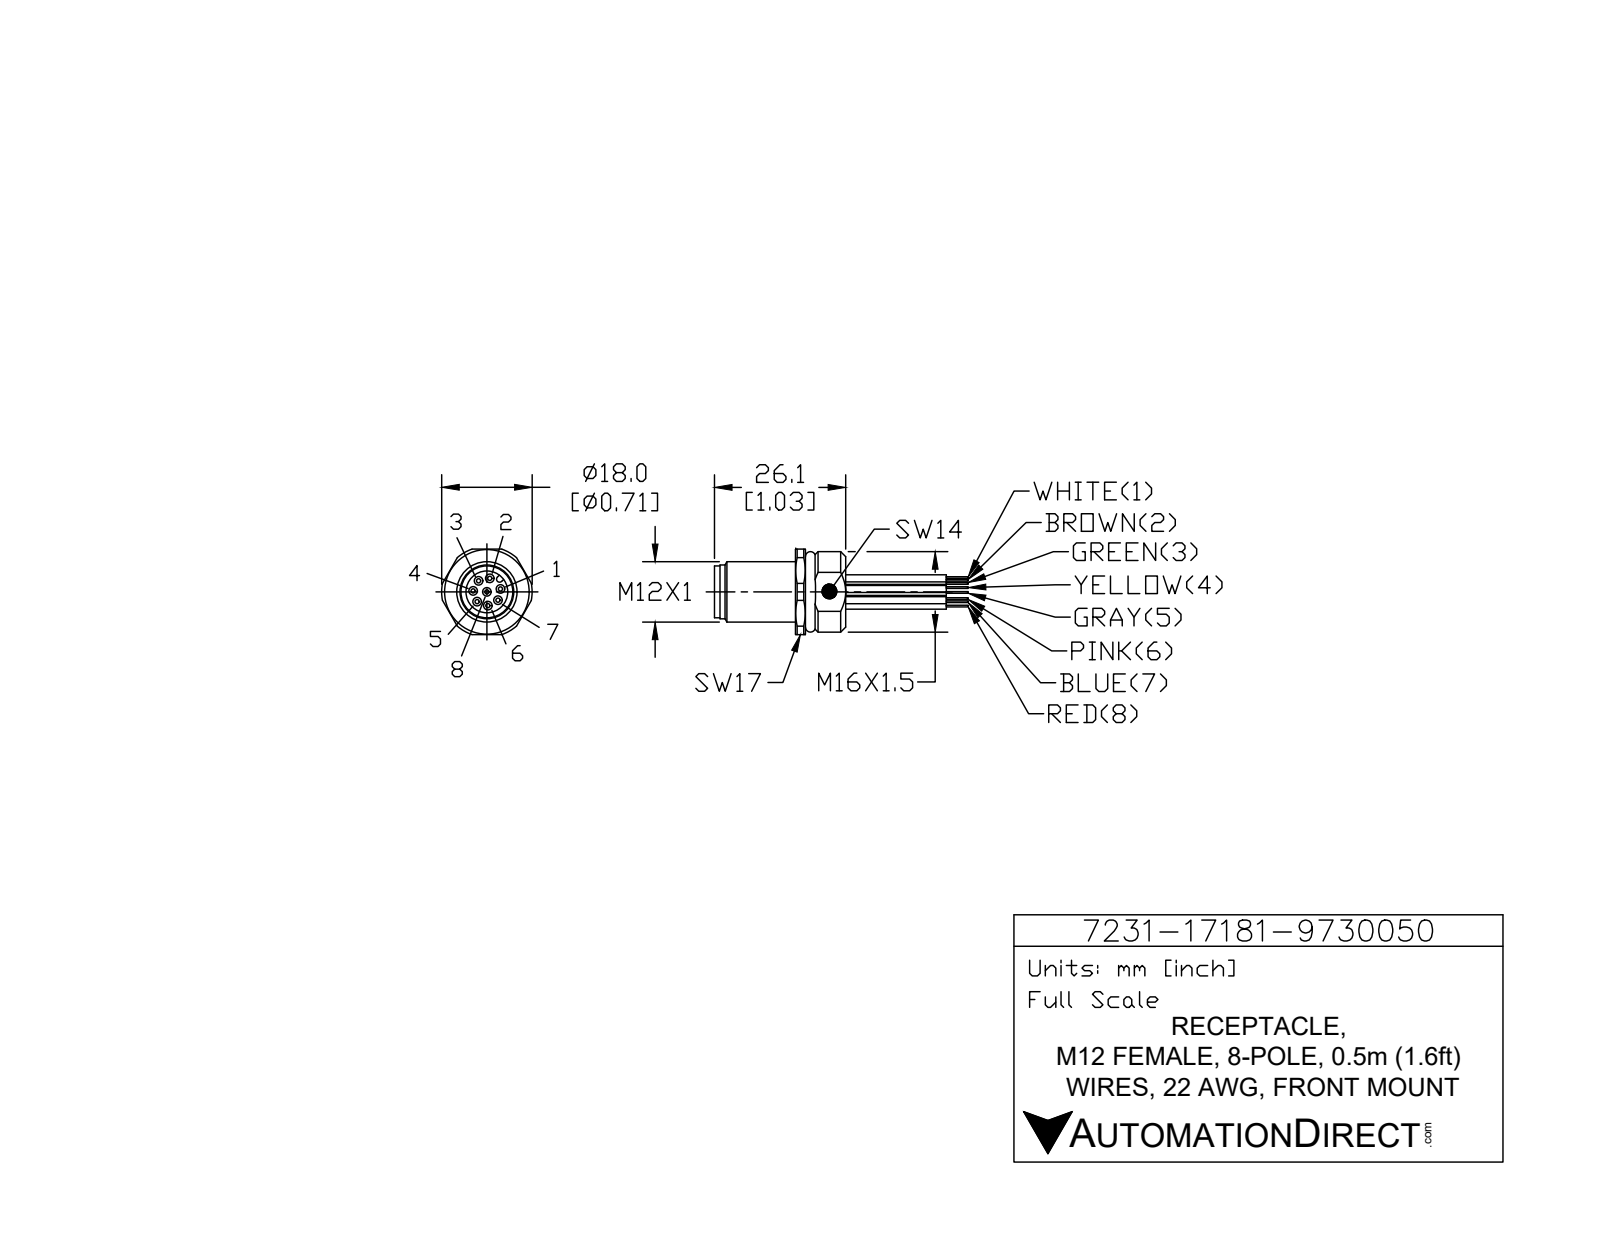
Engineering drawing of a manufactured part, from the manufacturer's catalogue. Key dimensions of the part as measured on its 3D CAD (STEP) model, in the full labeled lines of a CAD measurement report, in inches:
Part name (STEP PRODUCT): 7231-17181-9730050
STEP written by: SolidWorks 2015 (AUTOMOTIVE_DESIGN)
Units: inches
Bodies: 1 solid, 145 faces (35 planar, 53 cylindrical, 57 other)
Overall size (bounding box): 1.677 × 0.709 × 0.669
Volume: 0.208 in³ · Surface area: 4.644 in²
Round holes (diameter × count): ⌀0.035 ×8, ⌀0.43 ×1, ⌀0.48 ×1, ⌀0.512 ×1
Round bosses / shafts (diameter × count): ⌀0.055 ×8, ⌀0.531 ×1, ⌀0.319 ×1
Partial cylindrical surfaces — rounded edges, fillets, slot ends (radius × count): R0.026 ×1, R0.315 ×1, R0.354 ×1
Main face-to-face distances: 0.354, 0.496, 0.276, 0.079, 0.22, 0.142, 0.551, 0.85, 0.575, 0.669
Hole centre spacings: 0.108, 0.163, 0.207, 0.214, 0.089, 0.09, 0.09, 0.183
